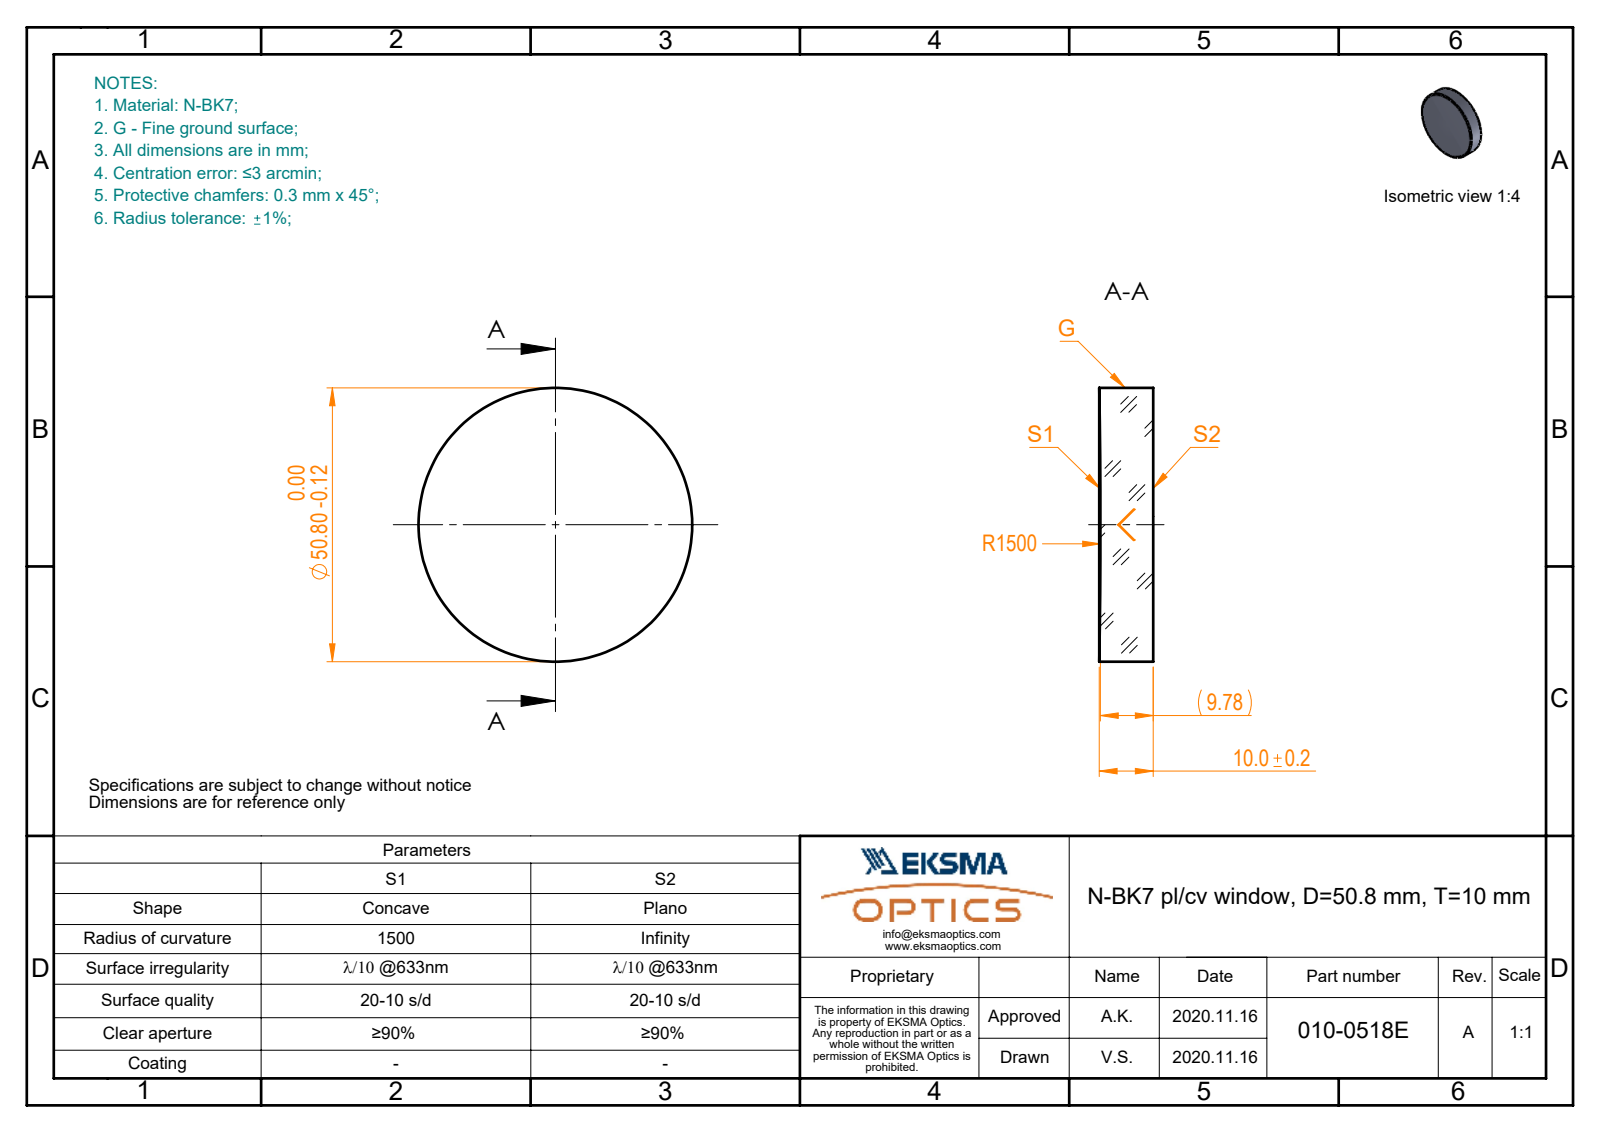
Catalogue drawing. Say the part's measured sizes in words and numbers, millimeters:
The part is named "010-0518E_N-BK7_PCV_window". Its 3-D file was written by "SolidWorks 2019 (CONFIG_CONTROL_DESIGN)". It is 1 solid with 5 faces: 1 planar, 2 cylindrical and 2 other. Overall it measures 50.8 by 50.8 by 10 millimeters. Its volume is 20 050 cubic millimeters and its surface area 5 650 square millimeters. Round bosses or shafts: 1 of diameter 50.8.
